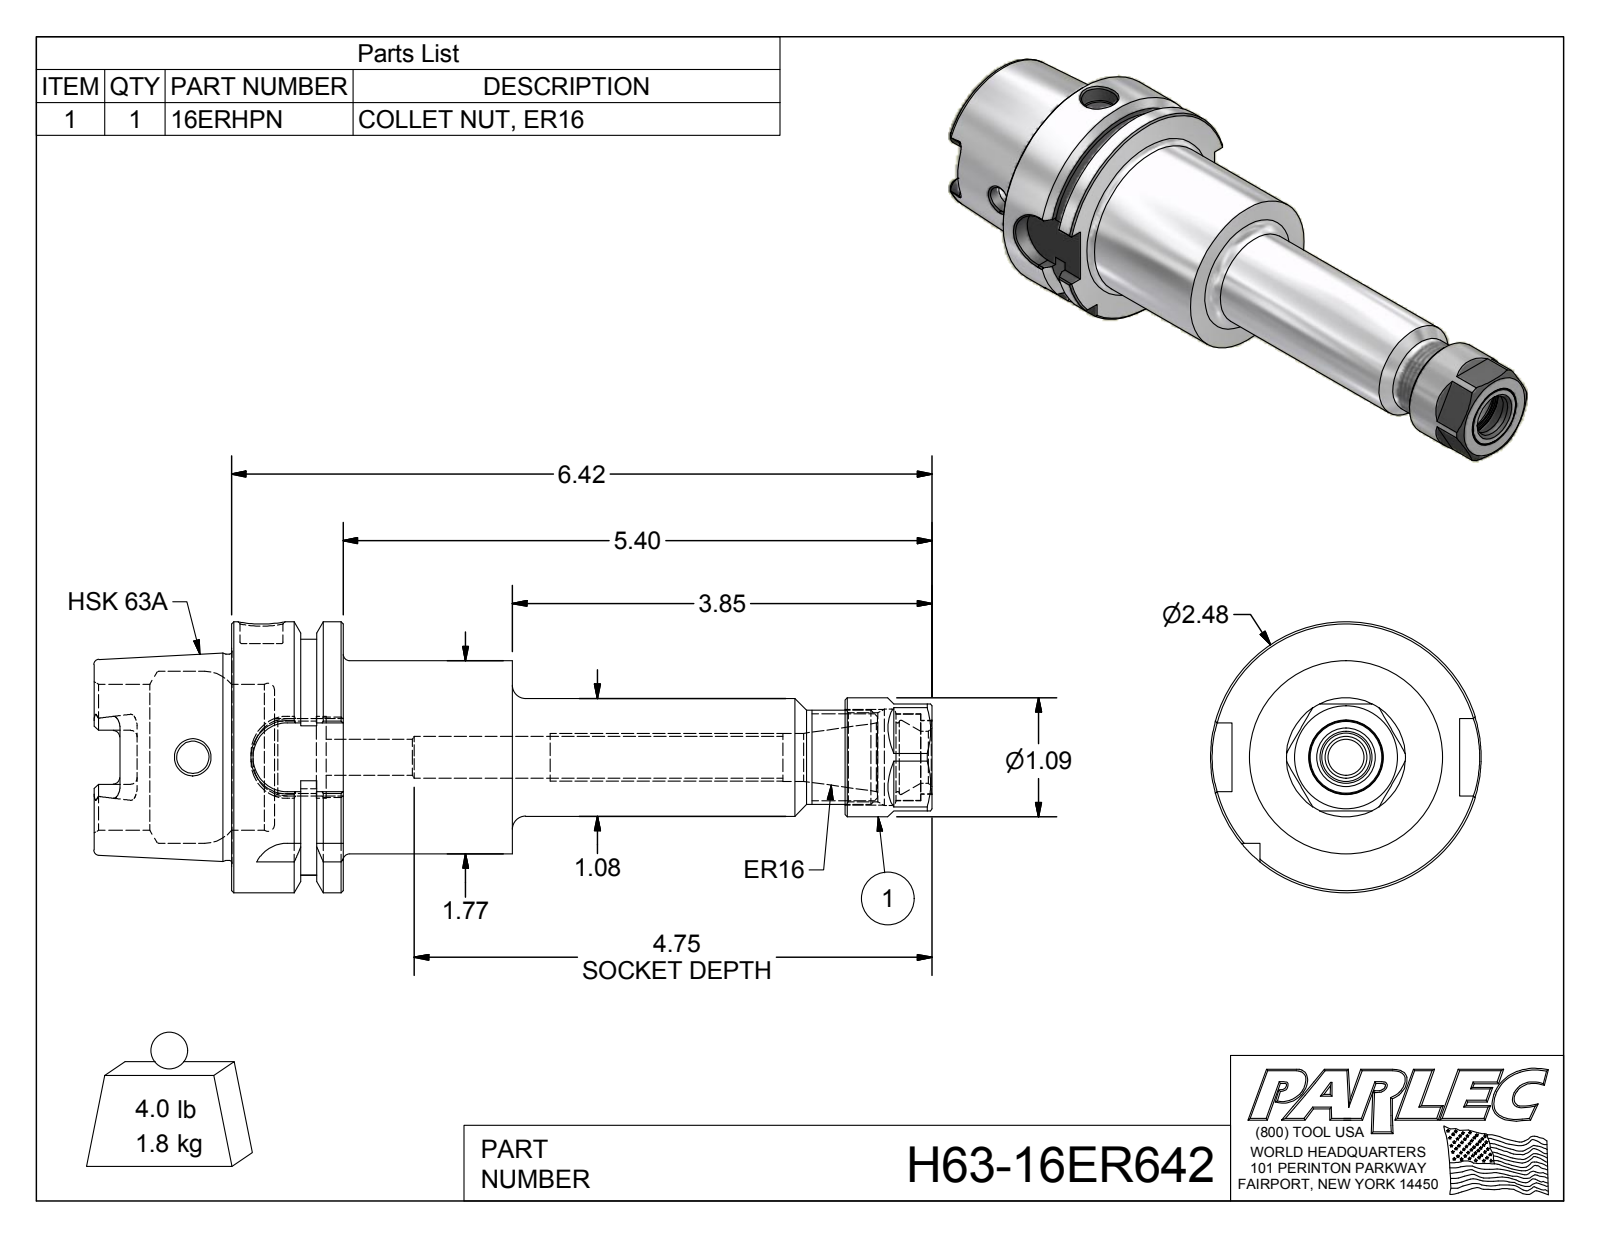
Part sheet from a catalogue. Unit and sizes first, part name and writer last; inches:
Units: inches
Overall size (bounding box): 7.68 × 2.48 × 2.48
Round holes (diameter × count): ⌀0.295 ×1, ⌀0.331 ×1, ⌀0.383 ×1, ⌀0.394 ×1, ⌀0.44 ×1, ⌀0.474 ×1, ⌀0.63 ×1, ⌀0.666 ×1, ⌀0.674 ×1, ⌀0.68 ×1, ⌀0.749 ×1, ⌀0.794 ×1
Round bosses / shafts (diameter × count): ⌀2.48 ×1, ⌀1.891 ×1, ⌀1.77 ×1, ⌀1.092 ×1, ⌀1.08 ×1, ⌀0.866 ×1, ⌀0.79 ×1, ⌀0.67 ×1
Partial cylindrical surfaces — rounded edges, fillets, slot ends (radius × count): R0.059 ×6, R0.113 ×4, R0.315 ×4, R1.083 ×1
Main face-to-face distances: 1.024, 2.575, 1.552, 0.241, 0.389, 0.394, 0.63, 2.181, 1.26, 1.654
Volume: 11.34 in³ · Surface area: 67.37 in²
Bodies: 3 solids, 184 faces (73 planar, 47 cylindrical, 64 other)
Part name (STEP PRODUCT): H63-16ER642; H63-16ER6-1; 16ERHPN
STEP written by: Autodesk Inventor 2012 (AUTOMOTIVE_DESIGN)
